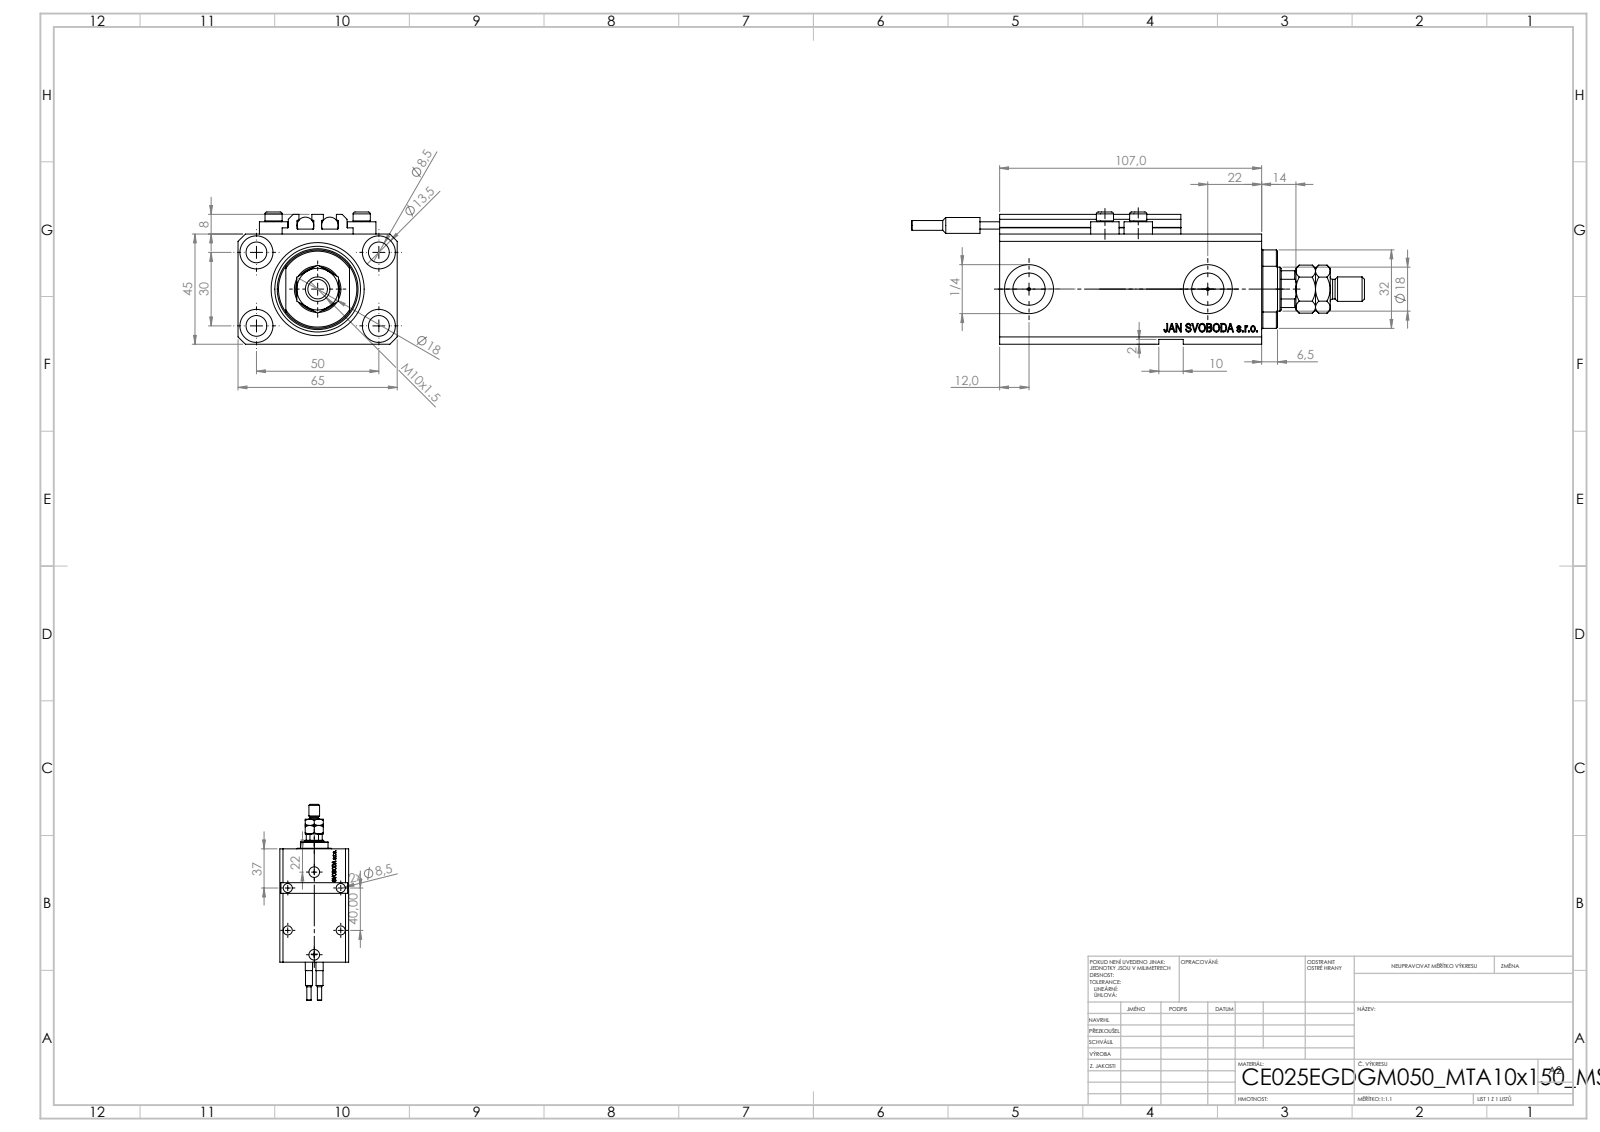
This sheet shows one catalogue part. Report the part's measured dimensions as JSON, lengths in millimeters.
{"part_name": "V250CE_VC_E; V250CE_E_Body; SWITCH_V250CE; ALLEN BOLT V250CE (+2 more)", "step_written_by": "SolidWorks 2019 (CONFIG_CONTROL_DESIGN)", "units": "millimeters", "bodies": {"solids": 11, "faces": 1204, "planar": 562, "cylindrical": 174, "other": 468}, "overall_size": [185, 65, 54], "volume_mm3": 277842, "surface_area_mm2": 82501, "round_holes": [[8.5, 9], [1.25, 4], [4, 4], [13.5, 4], [10, 2], [13.16, 2], [20, 2], [18, 1], [25, 1], [38, 1]], "round_bosses_or_shafts": [[11.6, 4], [7, 4], [6.8, 2], [6.5, 2], [4, 2], [10, 1], [8, 1]], "partial_cylinders_radius": [[0.2, 10], [8.5, 1], [16, 1]], "face_to_face_distances": [45, 65, 14, 2, 47, 93, 3, 107, 24, 6.9], "hole_center_spacings": [29.15, 50, 13.6, 14.76, 15.12, 27.51, 27.89, 30]}
